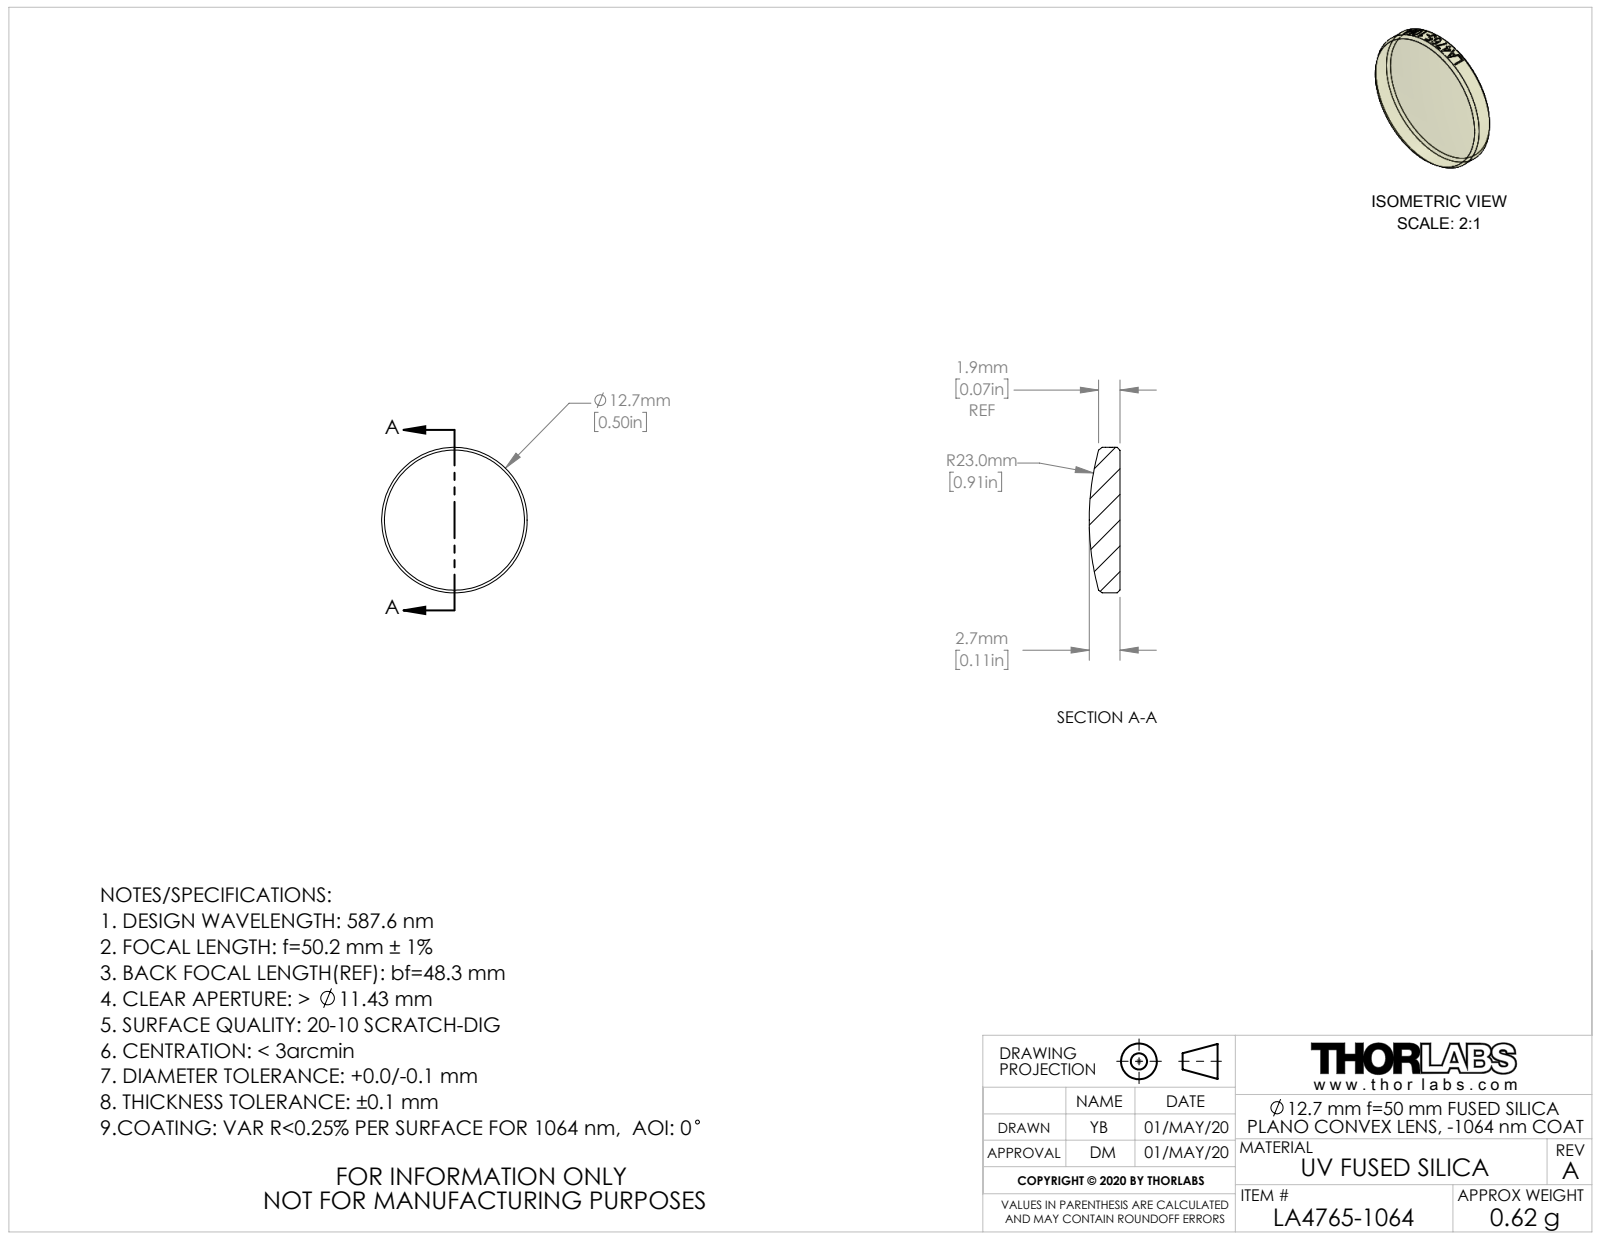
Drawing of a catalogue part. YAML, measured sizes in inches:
part_name: "CTN015557-E0W"
step_written_by: "SolidWorks 2018 (AUTOMOTIVE_DESIGN)"
units: inches
bodies: {solids: 1, faces: 26, planar: 1, cylindrical: 19, other: 6}
overall_size: [0.5, 0.5, 0.106]
volume: 0.017
surface_area: 0.493
round_bosses_or_shafts:
  - {diameter: 0.5, count: 1}
